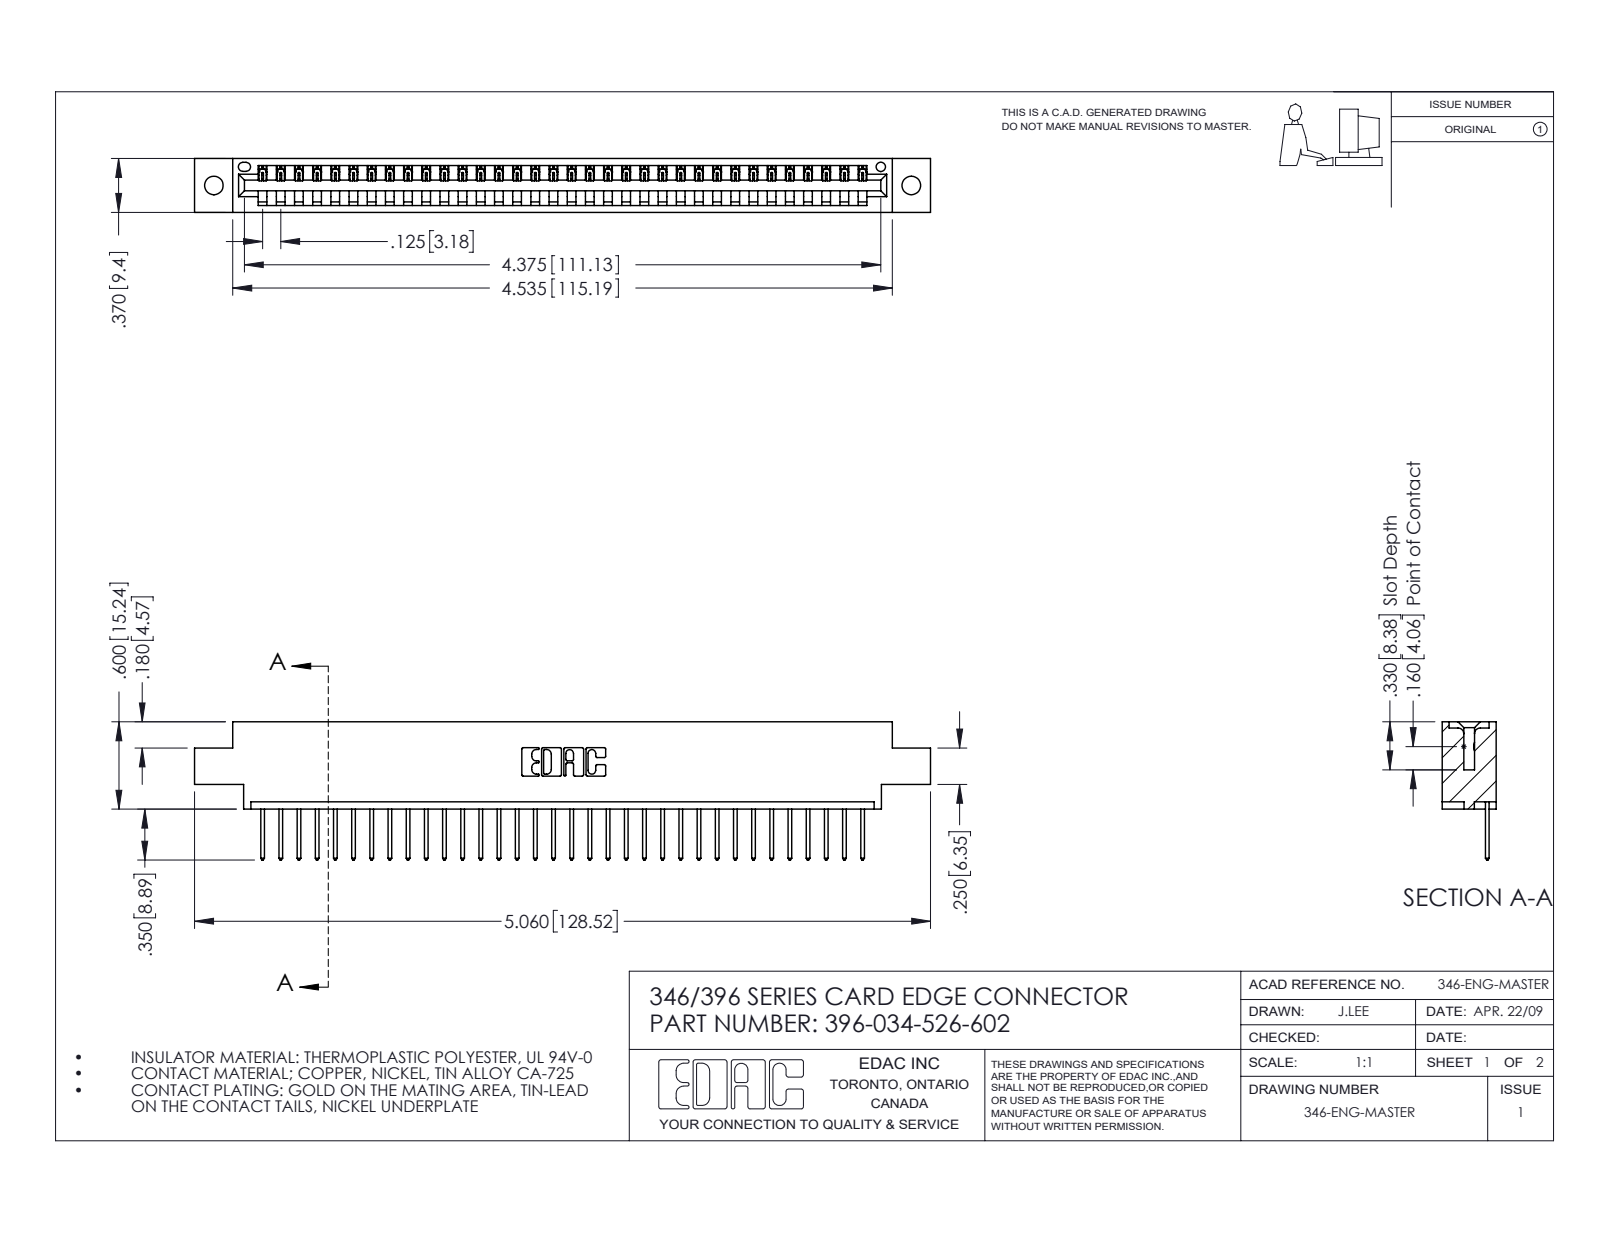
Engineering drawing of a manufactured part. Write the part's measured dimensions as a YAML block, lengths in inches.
part_name: "396-034-526-602; 345-292-001_345-293-126; 346 Part_0.170 Offset - 0.128 Dia"
step_written_by: "SolidWorks 2016 (CONFIG_CONTROL_DESIGN)"
units: inches
bodies: {solids: 35, faces: 2098, planar: 1440, cylindrical: 658, other: 0}
overall_size: [5.06, 0.95, 0.37]
volume: 0.734
surface_area: 22.95
round_holes:
  - {diameter: 0.128, count: 2}
  - {diameter: 0.064, count: 1}
partial_cylinders:
  - {radius: 0.006, count: 68}
  - {radius: 0.01, count: 68}
  - {radius: 0.01, count: 22}
  - {radius: 0.007, count: 6}
  - {radius: 0.031, count: 6}
  - {radius: 0.026, count: 3}
  - {radius: 0.031, count: 2}
  - {radius: 0.04, count: 2}
face_to_face_distances: [0.048, 0.322, 0.37, 0.25, 0.072, 0.298, 0.025, 0.148, 0.222, 0.1]
hole_center_spacings: [0.246, 4.587, 4.795]
